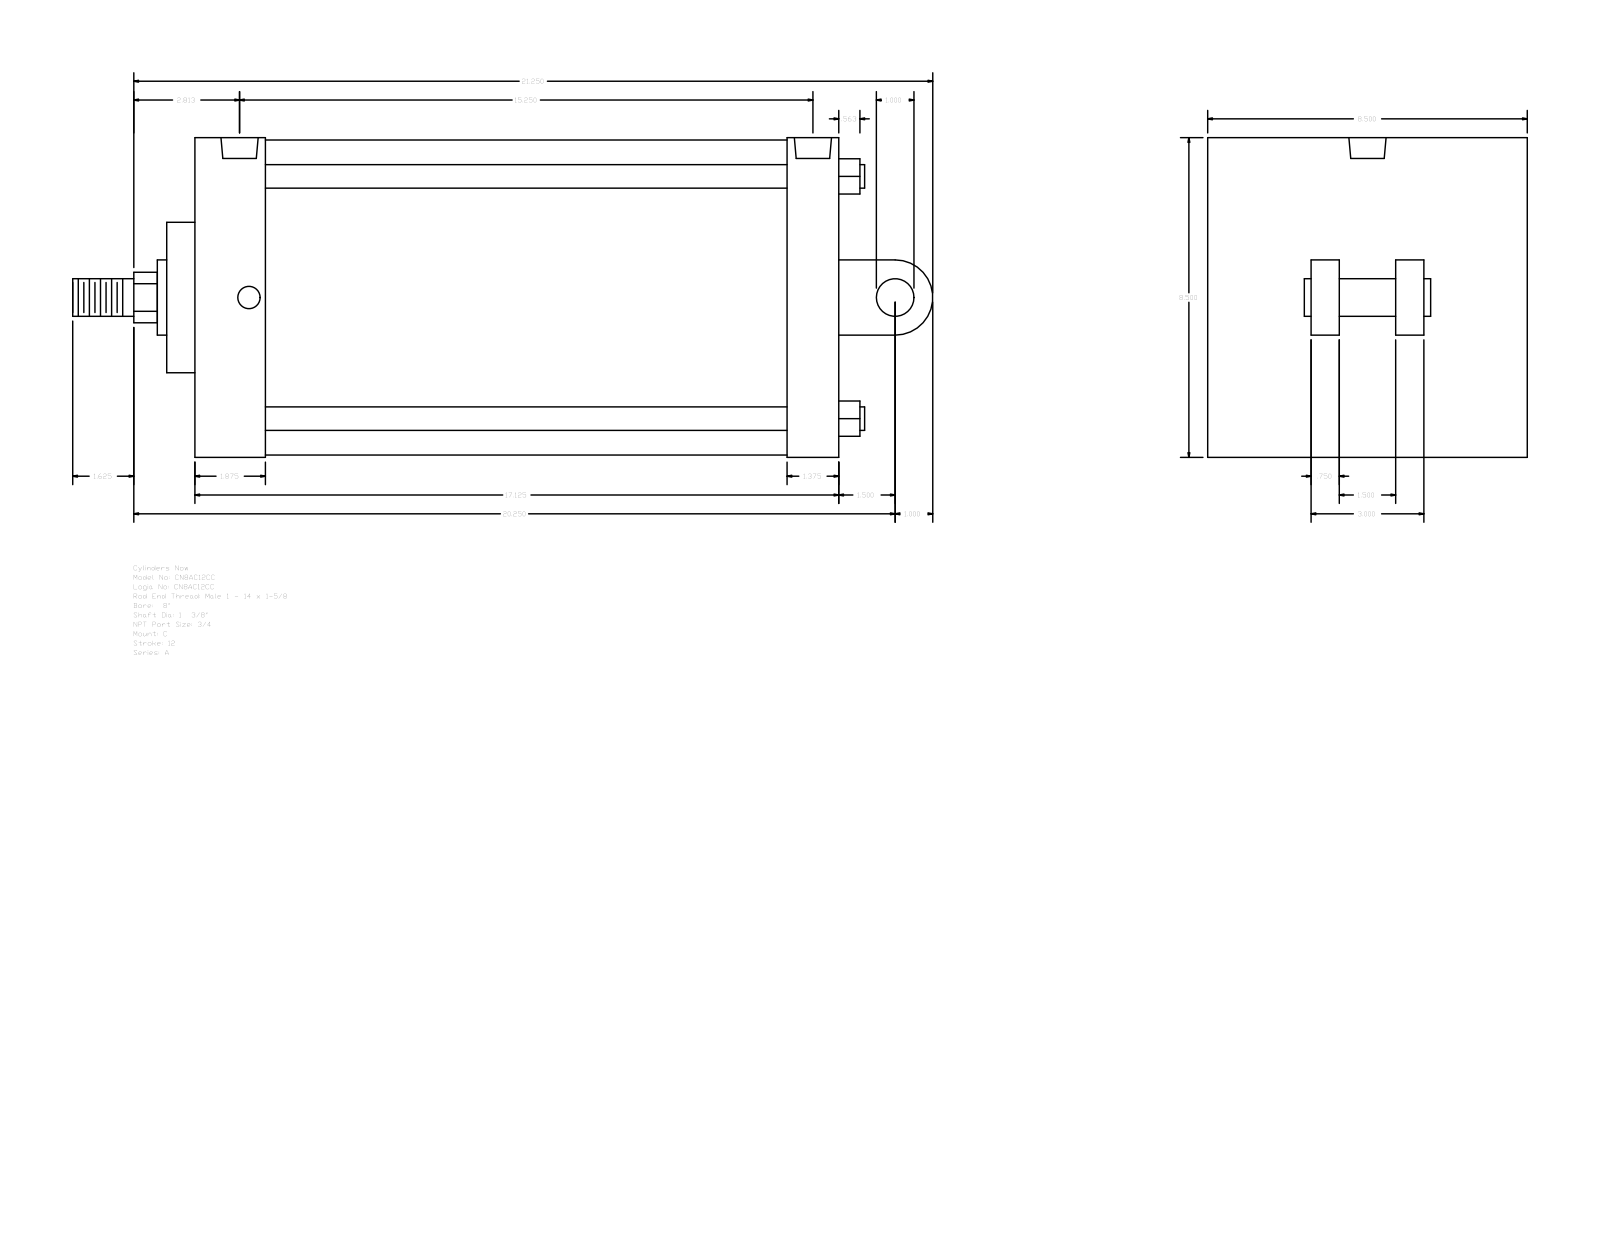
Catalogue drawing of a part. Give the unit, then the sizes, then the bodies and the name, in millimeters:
Units: millimetres
Overall size (bounding box): 581.02 × 215.9 × 215.9
Round holes (diameter × count): ⌀15.08 ×4, ⌀25.12 ×2
Round bosses / shafts (diameter × count): ⌀15.88 ×4, ⌀25.4 ×2, ⌀212.72 ×1, ⌀50.8 ×1, ⌀34.92 ×1
Partial cylindrical surfaces — rounded edges, fillets, slot ends (radius × count): R17.06 ×1, R25.4 ×1
Main face-to-face distances: 434.98, 215.9, 57.15, 47.63, 387.35, 400.05, 352.42, 34.93, 88.9, 69.85
Hole centre spacings: 6.35, 374.65, 381, 387.35
Bodies: 0 solids, 104 faces (75 planar, 29 cylindrical, 0 other)
Part name (STEP PRODUCT): A_C__0800_1.375
STEP written by: GSSL Pune (CONFIG_CONTROL_DESIGN)
